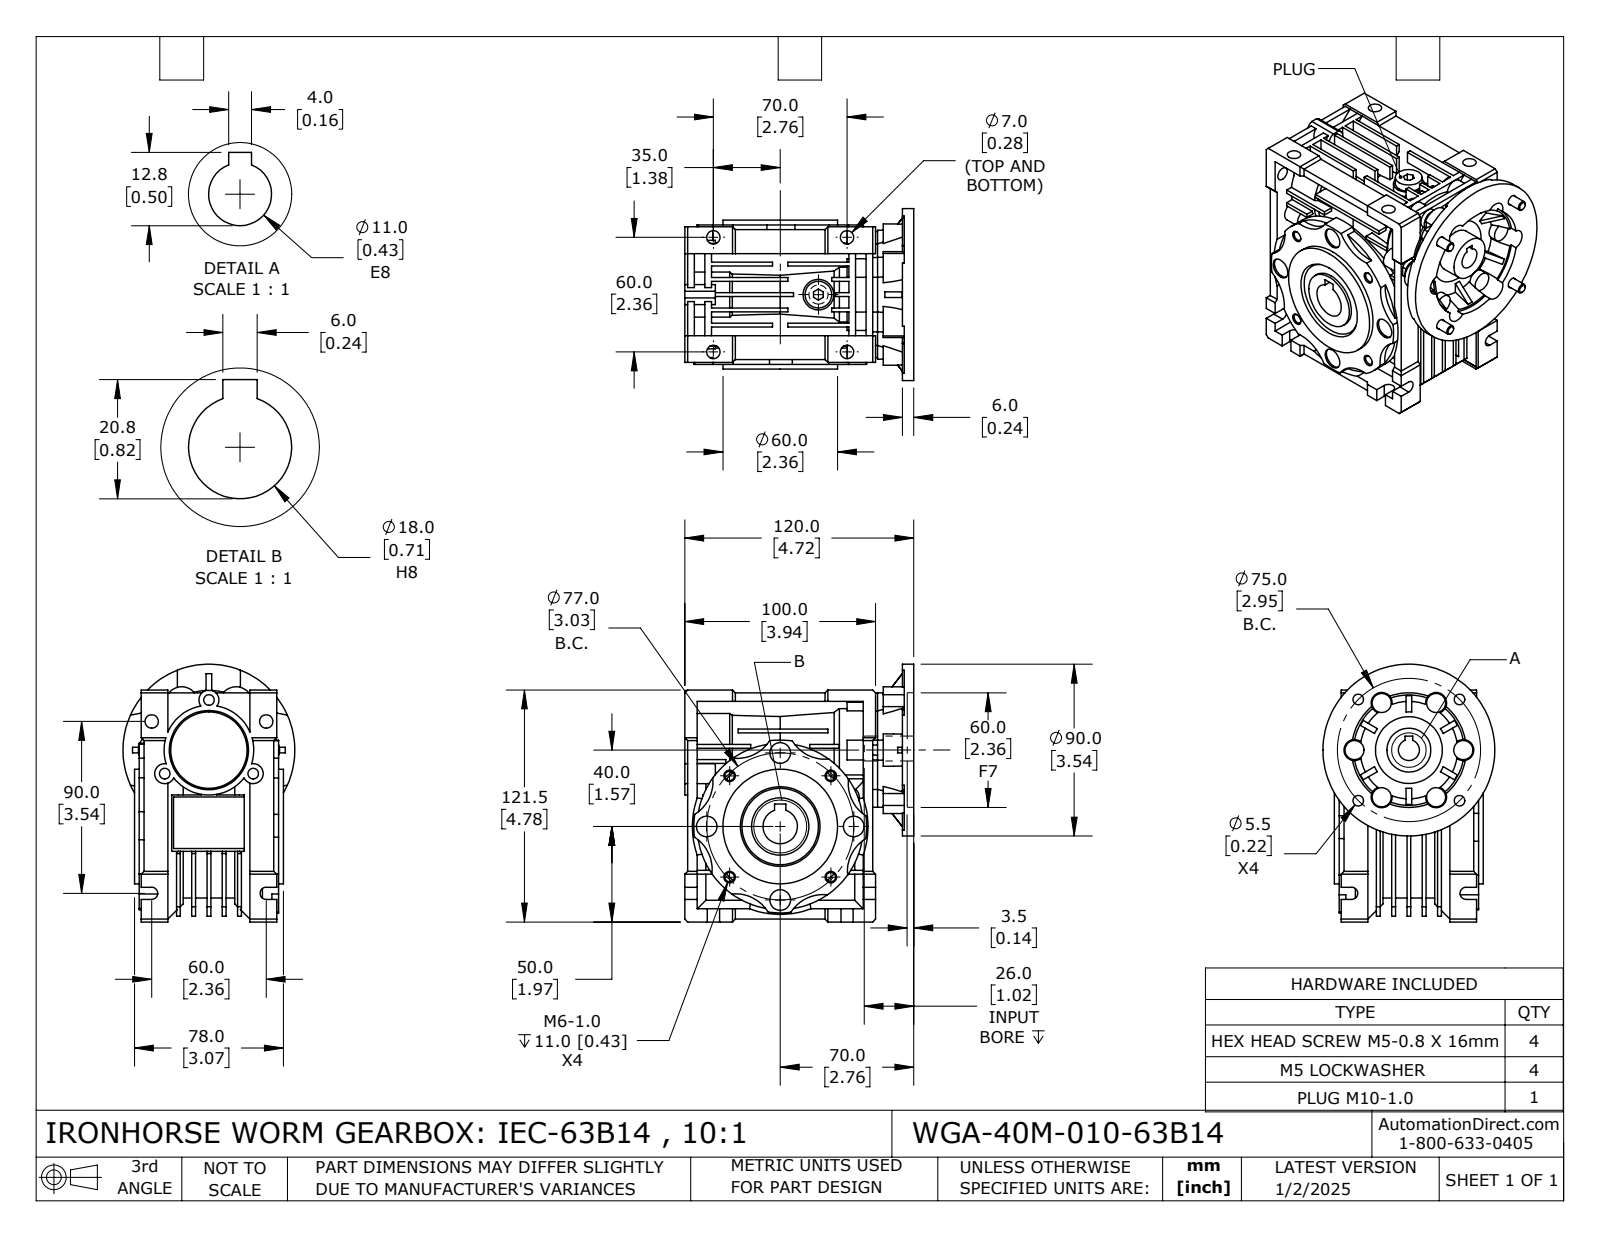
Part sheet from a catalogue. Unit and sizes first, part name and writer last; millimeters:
Units: millimetres
Overall size (bounding box): 135 × 127.7 × 90
Round holes (diameter × count): ⌀7 ×6, ⌀4.92 ×4, ⌀5.1 ×4, ⌀5.5 ×4, ⌀10.8 ×4, ⌀5.55 ×3, ⌀9 ×1, ⌀11 ×1, ⌀11.5 ×1, ⌀18 ×1, ⌀23 ×1, ⌀28 ×1
Round bosses / shafts (diameter × count): ⌀10 ×6, ⌀9.2 ×4, ⌀5 ×4, ⌀90 ×1, ⌀75 ×1, ⌀60 ×1, ⌀54 ×1, ⌀47 ×1
Partial cylindrical surfaces — rounded edges, fillets, slot ends (radius × count): R5.25 ×9, R20 ×8, R3.2 ×6, R5.22 ×6, R5.5 ×6, R8.5 ×6, R5.51 ×4, R30 ×1
Main face-to-face distances: 8, 6, 2, 1.5, 16, 10, 5, 14, 2.5, 19
Hole centre spacings: 29.1, 37.5, 53.04, 70.22, 33.54, 38.5, 54.45, 75.01
Volume: 667 307 mm³ · Surface area: 163 100 mm²
Bodies: 14 solids, 1003 faces (564 planar, 307 cylindrical, 132 other)
Part name (STEP PRODUCT): WGA-40M-010-63B14
STEP written by: SolidWorks 2024 (CONFIG_CONTROL_DESIGN)
